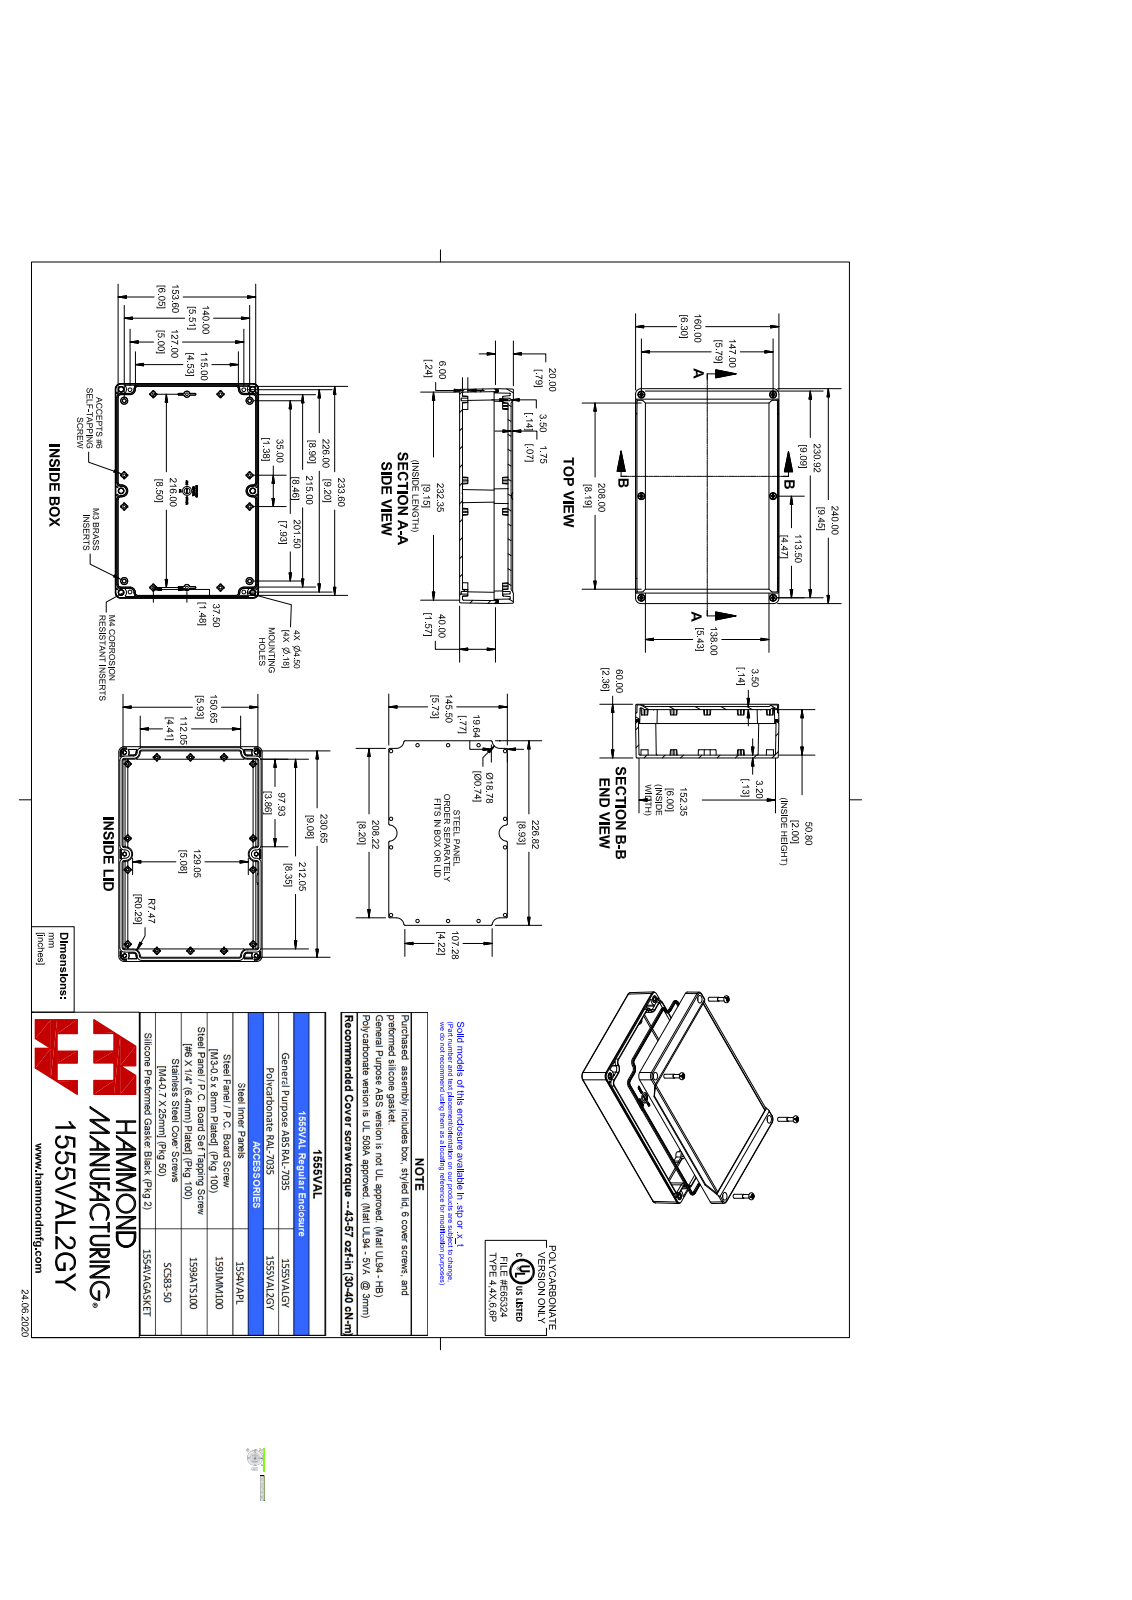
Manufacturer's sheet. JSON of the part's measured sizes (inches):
{"part_name": "1555VAL2GY", "step_written_by": "SolidWorks 2021 (AUTOMOTIVE_DESIGN)", "units": "inches", "bodies": {"solids": 19, "faces": 2398, "planar": 926, "cylindrical": 468, "other": 1004}, "overall_size": [9.449, 6.299, 2.362], "volume_in3": 26.31, "surface_area_in2": 436.6, "round_holes": [[0.128, 6], [0.097, 4], [0.181, 4]], "round_bosses_or_shafts": [[0.272, 6], [0.25, 6], [0.218, 6], [0.21, 6], [0.152, 6], [0.137, 6], [0.19, 4], [0.154, 4]], "partial_cylinders_radius": [[0.02, 47], [0.012, 28], [0.039, 22], [0.1, 12], [0.195, 12], [0.059, 8], [0.236, 8], [0.031, 6]], "face_to_face_distances": [0.126, 0.138, 2, 2.126, 2.264, 2.138, 0.185, 6.114, 5.988, 9.449], "hole_center_spacings": [0.52, 3.969, 4.469, 5.672, 6.903, 7.312, 8.436, 10.152]}
